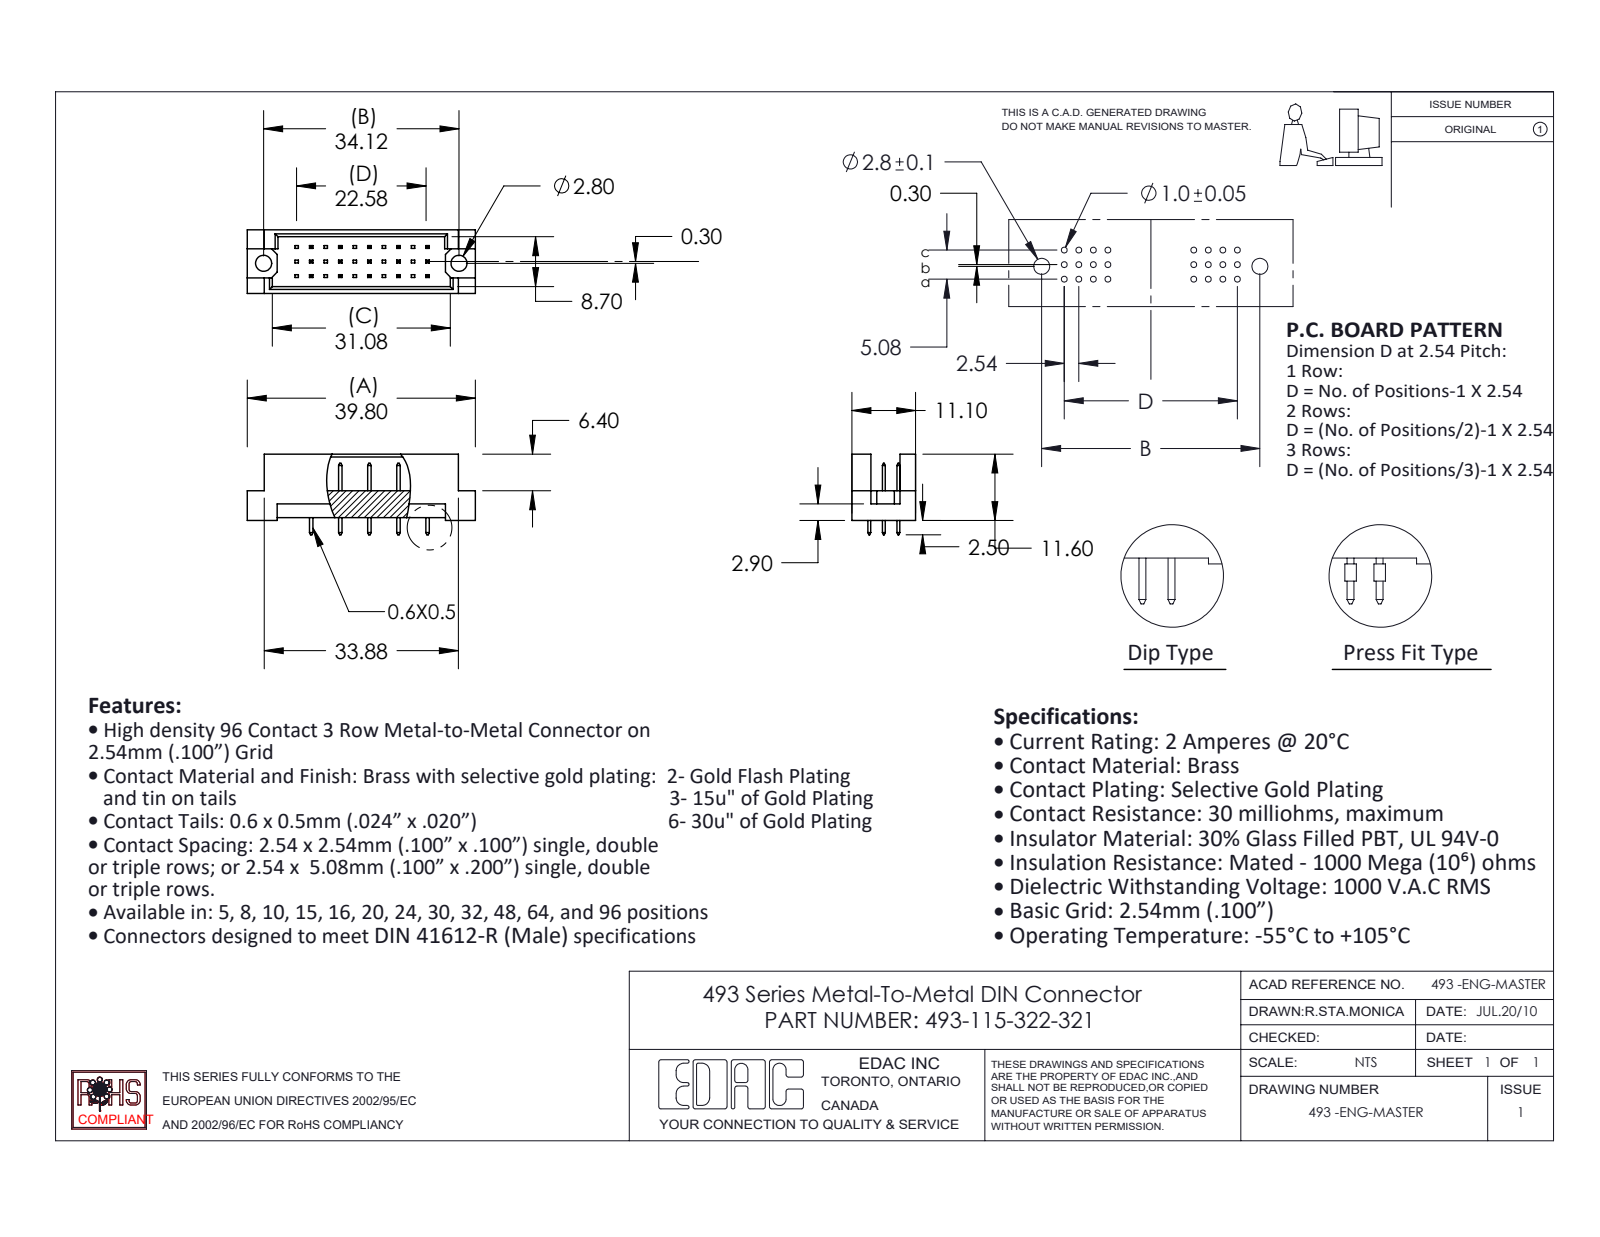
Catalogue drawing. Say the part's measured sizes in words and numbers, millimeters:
The part is named "493 Part_30; 493-115-322-322; 493-290_22". Its 3-D file was written by "SolidWorks 2020 (CONFIG_CONTROL_DESIGN)". It is 16 solids with 382 faces: 378 planar, 4 cylindrical and 0 other. Overall it measures 39.8 by 14.1 by 11.1 millimeters. Its volume is 2 428 cubic millimeters and its surface area 3 144 square millimeters. Round holes: 2 of diameter 2.8. The main face-to-face distances are 1.2, 9.9, 11.1, 5.08, 8.7, 0.5, 2.54, 4.7, 10.16, 2.4. The hole center spacings are 34.12.
